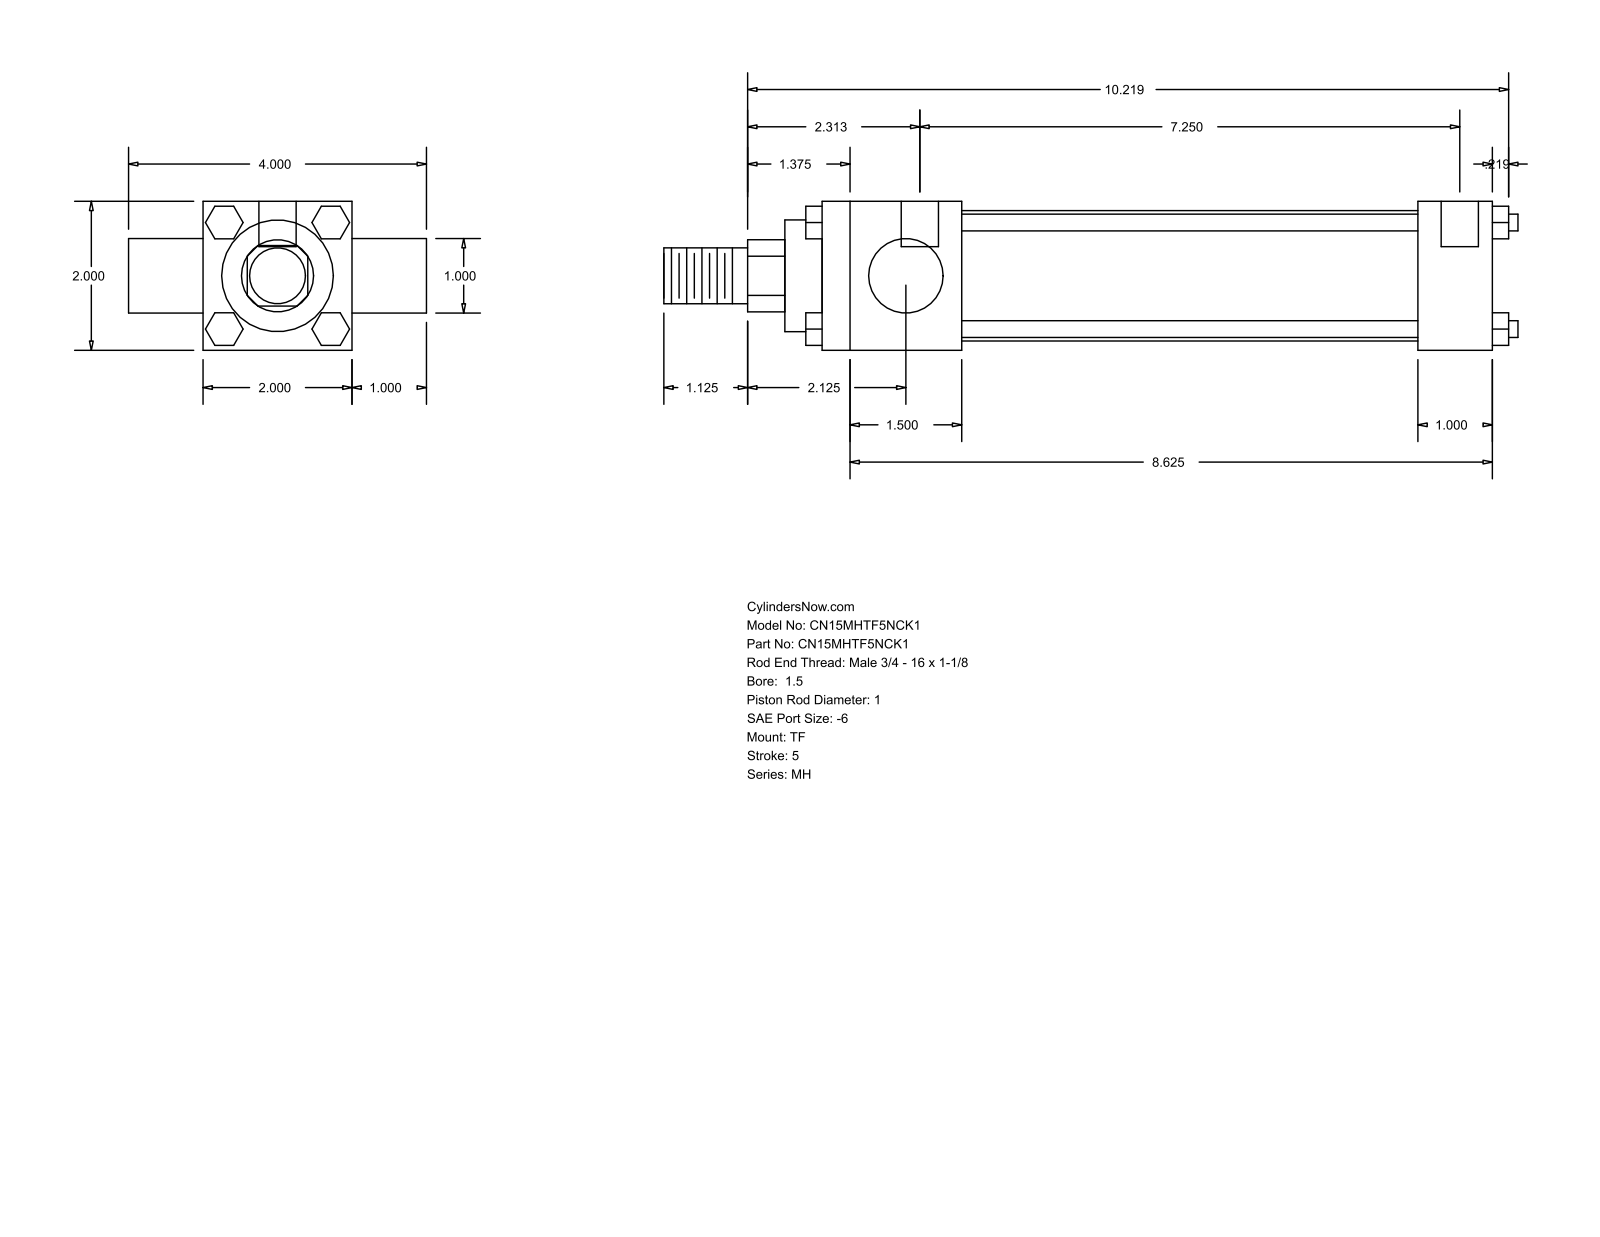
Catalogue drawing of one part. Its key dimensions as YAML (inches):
part_name: "MH_TF__0150_1"
step_written_by: "GSSL Pune (CONFIG_CONTROL_DESIGN)"
units: inches
bodies: {solids: 0, faces: 120, planar: 92, cylindrical: 28, other: 0}
overall_size: [11.469, 4, 2]
round_holes:
  - {diameter: 0.219, count: 3}
  - {diameter: 0.5, count: 2}
round_bosses_or_shafts:
  - {diameter: 0.225, count: 4}
  - {diameter: 1, count: 2}
  - {diameter: 1.75, count: 1}
  - {diameter: 1.5, count: 1}
  - {diameter: 0.75, count: 1}
partial_cylinders:
  - {radius: 0.484, count: 1}
face_to_face_distances: [2, 1, 9, 3, 1.875, 7.125, 8, 6.125, 4, 0.5]
hole_center_spacings: [0.125, 7.25, 7.375]
